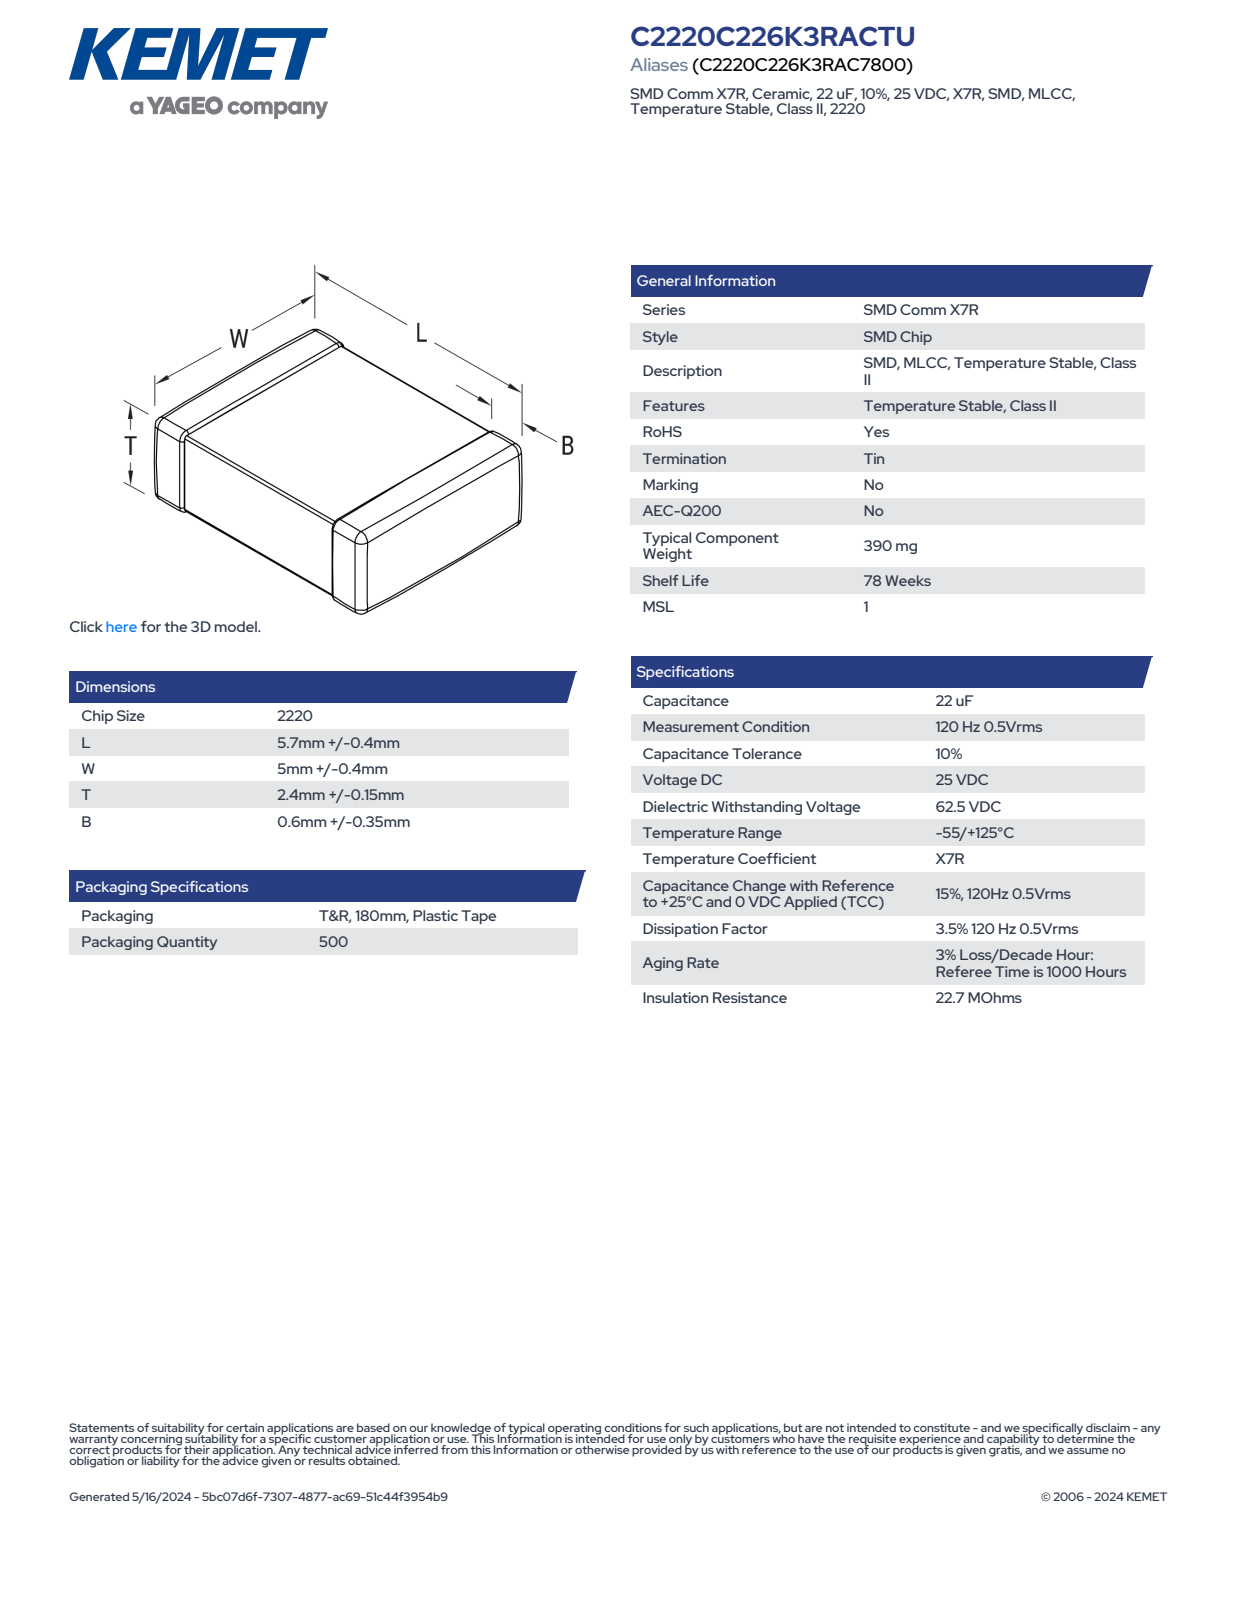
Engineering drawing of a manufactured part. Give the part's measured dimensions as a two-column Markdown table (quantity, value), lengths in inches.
| quantity | value |
| --- | --- |
| part name | CCS_CCSTDNOS_2220_L6.1W5.4T2.55B0.95 |
| STEP written by | SolidWorks 2014 (AUTOMOTIVE_DESIGN) |
| units | inches |
| bodies | 4 solids, 125 faces (71 planar, 38 cylindrical, 16 other) |
| overall size | 0.24 × 0.213 × 0.1 |
| volume | 0.005 in³ |
| surface area | 0.188 in² |
| partial cylindrical surfaces (radius × count) | 0.004 × 24 |
| main face-to-face distances | 0.092, 0.096, 0.24, 0.204, 0.1, 0.208, 0.213, 0.105, 0.108, 0.104 |
